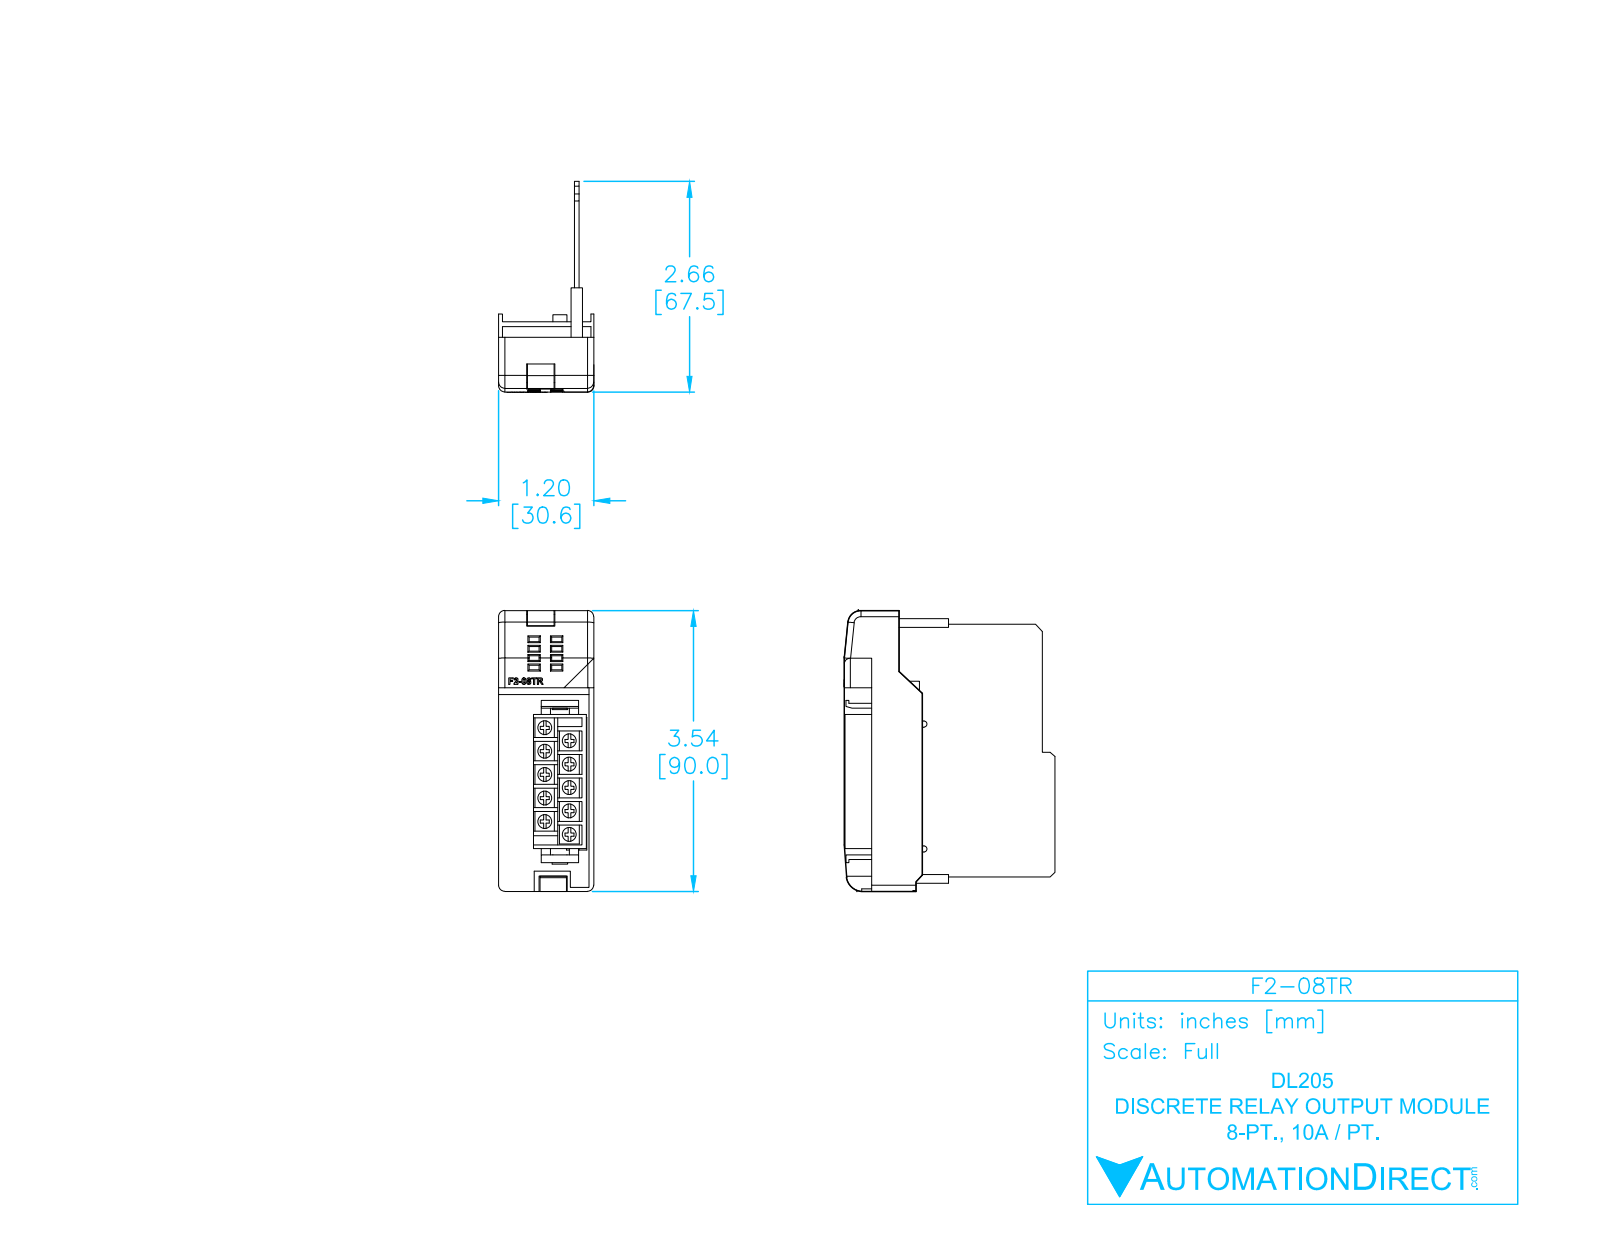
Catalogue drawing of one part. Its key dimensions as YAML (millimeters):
part_name: "F2-08TR_ModuleCase_light"
step_written_by: "SolidWorks 2009 (AUTOMOTIVE_DESIGN)"
units: millimeters
bodies: {solids: 6, faces: 565, planar: 402, cylindrical: 75, other: 88}
overall_size: [90, 67.61, 30.55]
volume: 25374
surface_area: 28531
round_bosses_or_shafts:
  - {diameter: 4.5, count: 10}
partial_cylinders:
  - {radius: 0.35, count: 16}
  - {radius: 2, count: 9}
  - {radius: 0.25, count: 2}
  - {radius: 1, count: 2}
  - {radius: 1.25, count: 2}
  - {radius: 4.12, count: 1}
  - {radius: 5.39, count: 1}
face_to_face_distances: [1.5, 4.72, 6.22, 2.37, 3.87, 2.35, 3.22, 0.85, 7.25, 8.14]
